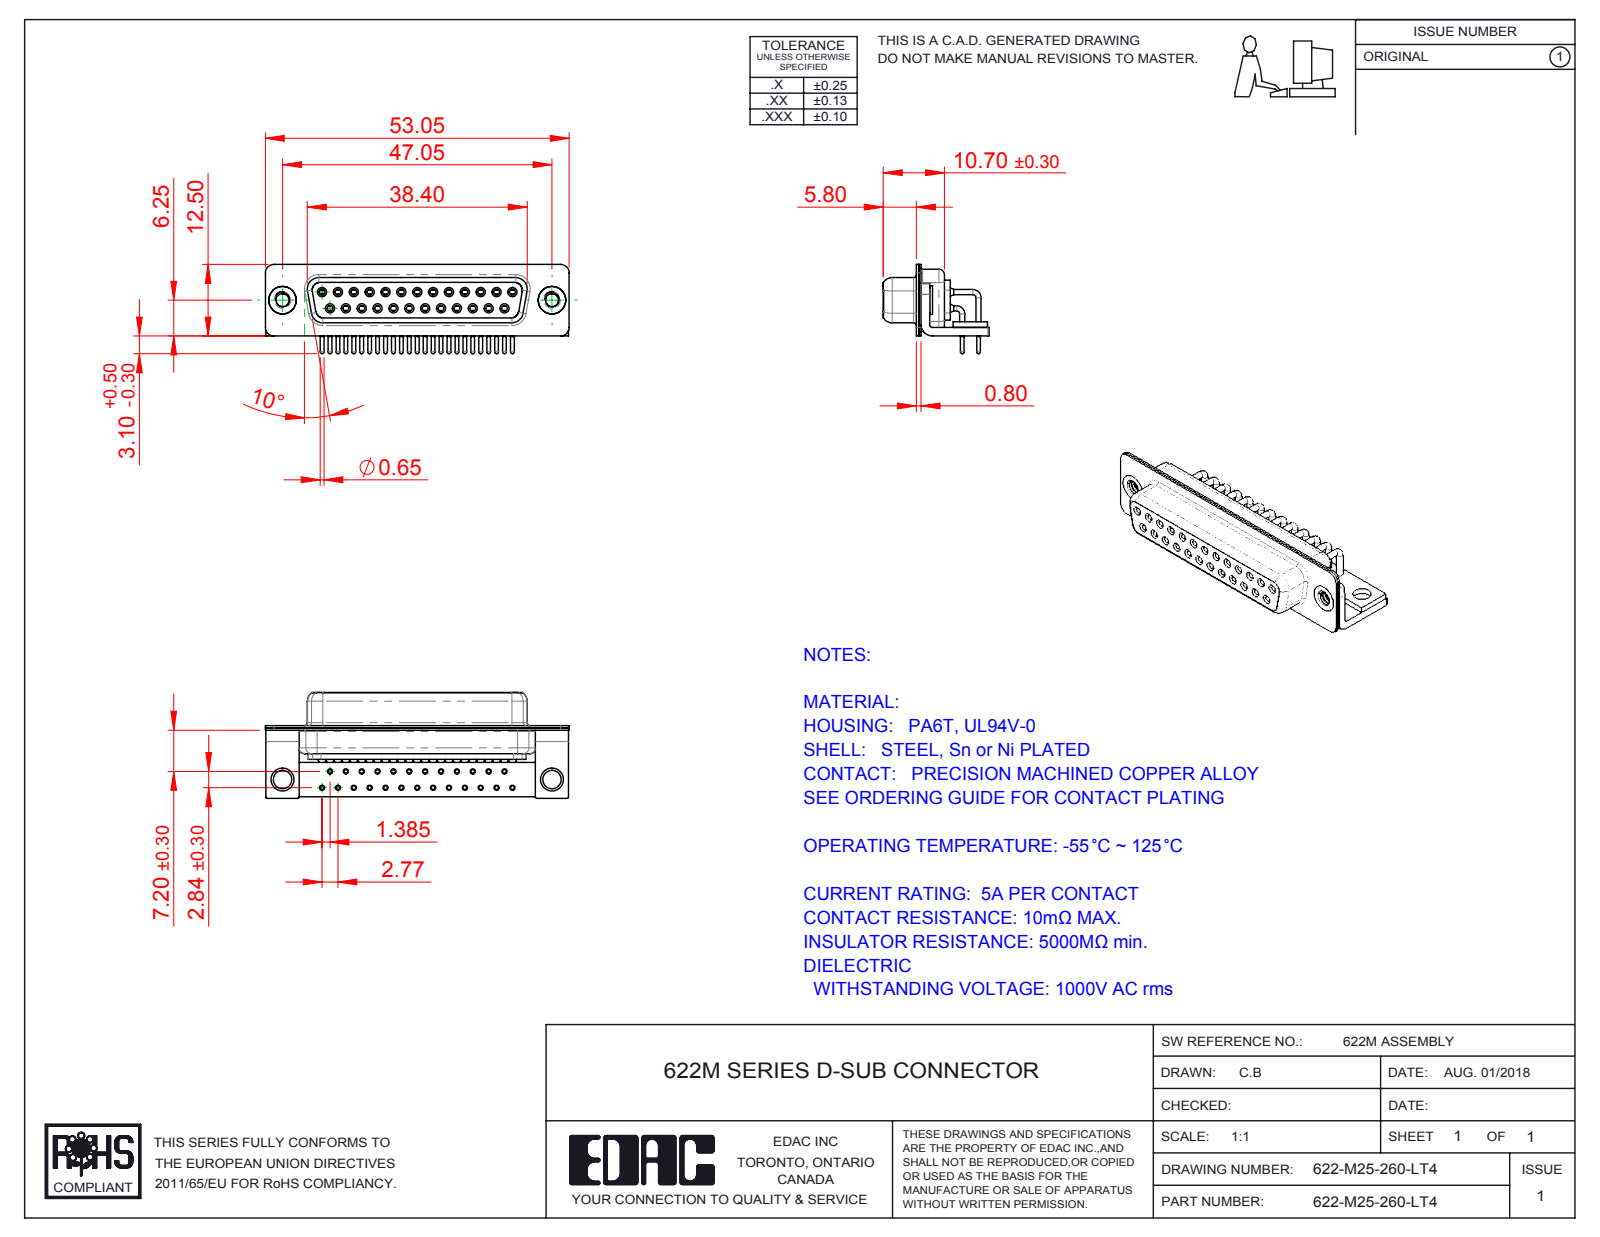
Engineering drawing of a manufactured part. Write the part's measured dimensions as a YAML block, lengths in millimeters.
part_name: "622M 4-40 Threaded Rivet_Stabilizer; 622M Contact Row 2; 622M Contact Row 1; 622M Shell Rear_25 Contacts (+5 more)"
step_written_by: "SolidWorks 2016 (CONFIG_CONTROL_DESIGN)"
units: millimeters
bodies: {solids: 33, faces: 1704, planar: 468, cylindrical: 784, other: 452}
overall_size: [53.05, 18.5, 15.6]
volume: 4362
surface_area: 10799
round_holes:
  - {diameter: 0.9, count: 25}
  - {diameter: 1, count: 25}
  - {diameter: 1.1, count: 25}
  - {diameter: 1.7, count: 25}
  - {diameter: 1.8, count: 25}
  - {diameter: 2, count: 25}
  - {diameter: 2.26, count: 2}
  - {diameter: 3.2, count: 2}
  - {diameter: 4, count: 2}
  - {diameter: 4.8, count: 2}
round_bosses_or_shafts:
  - {diameter: 0.9, count: 27}
  - {diameter: 1.6, count: 25}
  - {diameter: 1.5, count: 25}
  - {diameter: 0.65, count: 25}
  - {diameter: 5, count: 2}
  - {diameter: 4.9, count: 2}
partial_cylinders:
  - {radius: 0.25, count: 16}
  - {radius: 1.5, count: 16}
  - {radius: 2, count: 13}
  - {radius: 1.35, count: 8}
  - {radius: 1.6, count: 8}
  - {radius: 0.5, count: 5}
  - {radius: 0.6, count: 4}
  - {radius: 0.65, count: 4}
face_to_face_distances: [0.4, 2.3, 1.9, 1.45, 8.95, 0.85, 0.8, 6.2, 1, 9.35]
hole_center_spacings: [3.16, 2.77, 5.54, 8.31, 11.08, 13.85, 16.62, 5.04]
